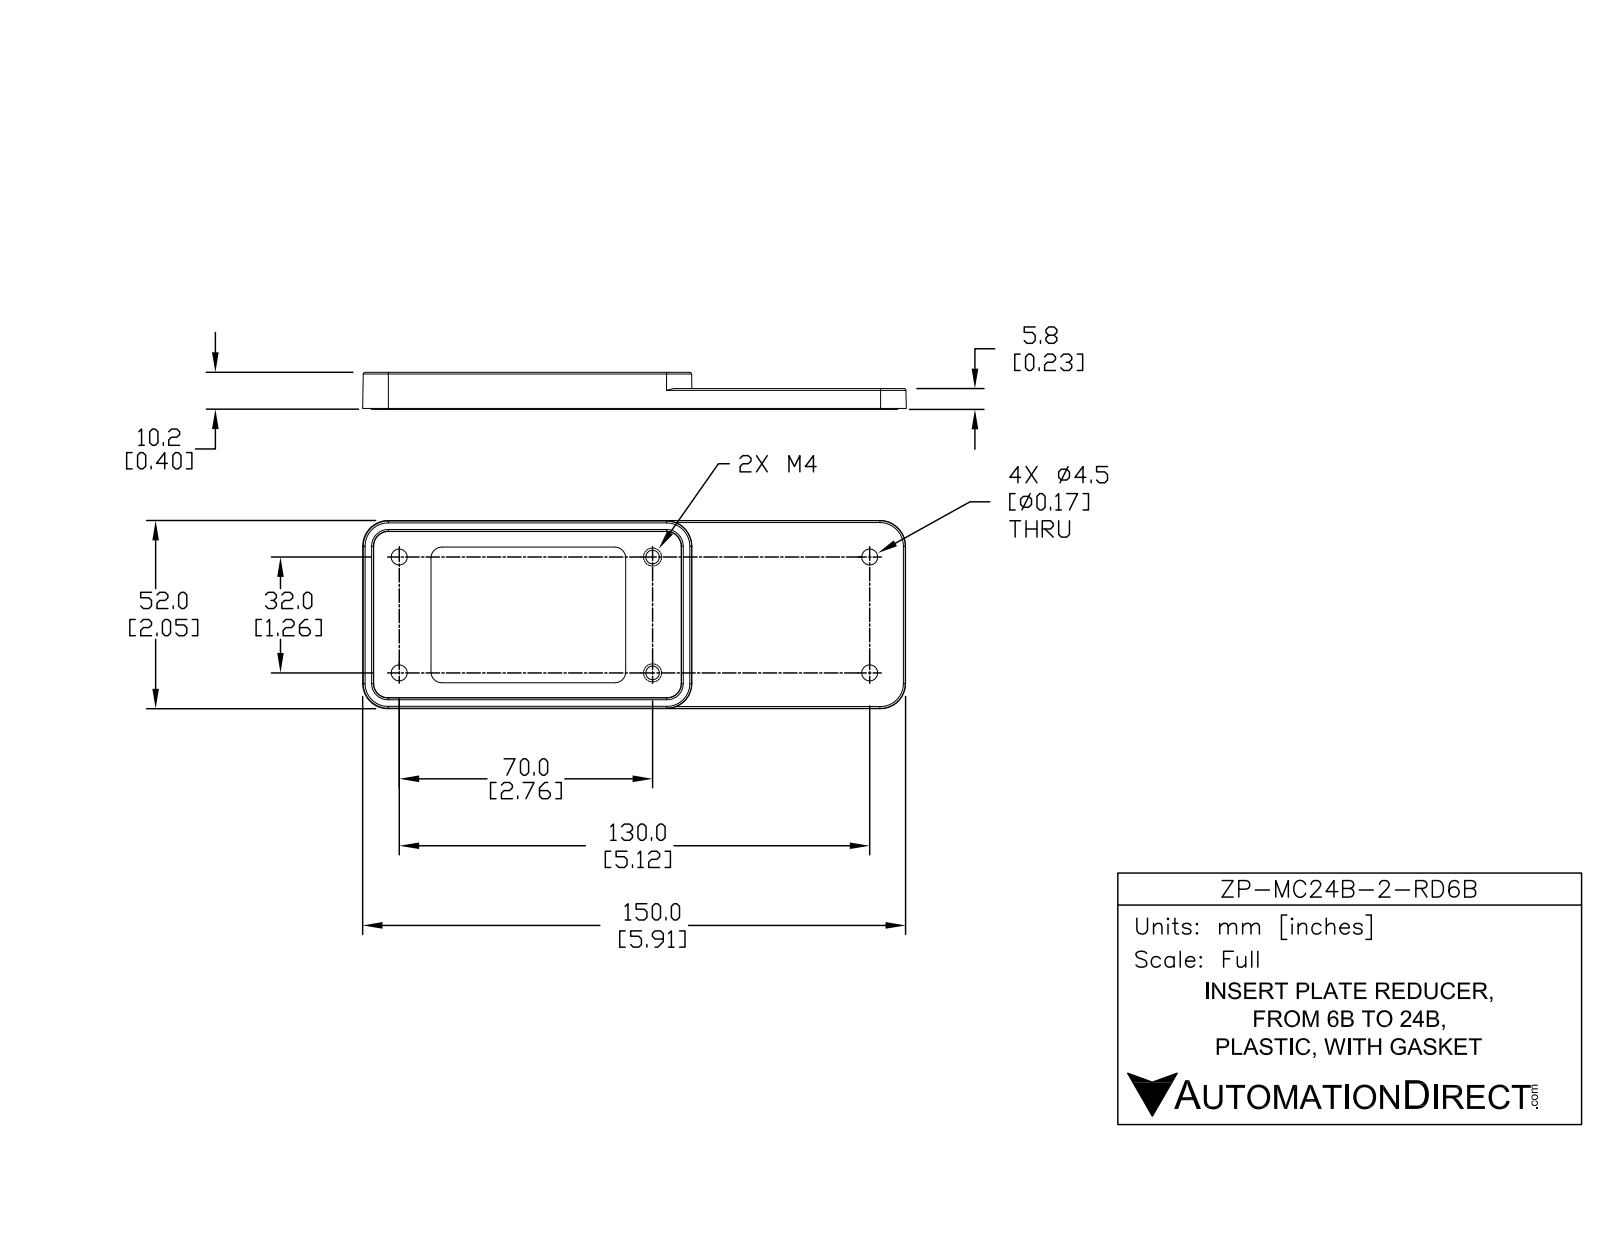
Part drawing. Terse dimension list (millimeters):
name: ZP-MC24B-2-RD6B
written by: SolidWorks 2014 (AUTOMOTIVE_DESIGN)
unit: mm
bodies: 1 solid, 161 faces (61 planar, 72 cylindrical, 28 other)
size: 150.19 × 52.19 × 10.25
volume: 27 700 mm³; area: 18 437 mm²
holes: 4× ⌀4.4, 2× ⌀3.75
rounds: 27× R0.5, 4× R1.5, 4× R3, 4× R4.2, 2× R1.5, 2× R1.52, 2× R5.5
face distances: 2.5, 3, 5.5, 3.25, 5.75, 49.05, 10.25, 10, 7, 4.5
hole spacings: 32, 60, 68, 70, 76.97, 130, 133.88
